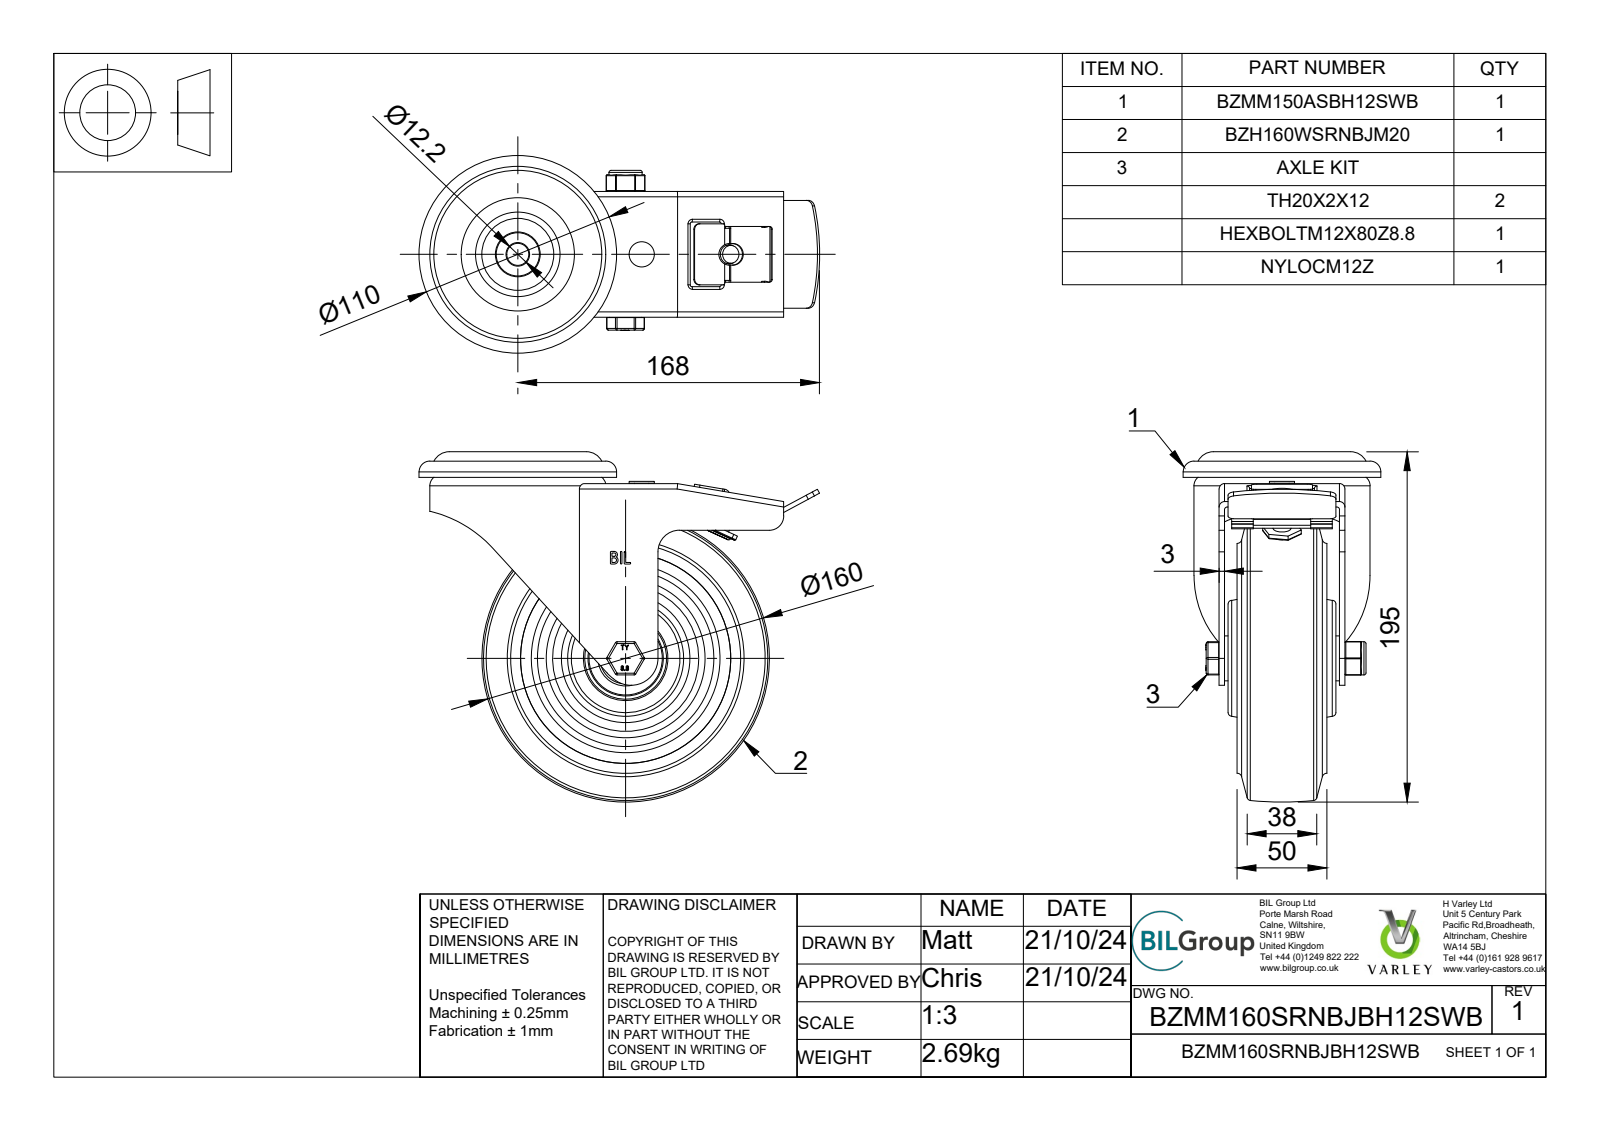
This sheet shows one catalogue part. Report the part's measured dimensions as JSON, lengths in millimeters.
{"part_name": "BZMM160SRNBJBH12SWB v3; BZMM150ASBH12SWB - 64 v1; ZINC PLATED, PRESSED STEEL TOP PLATE; ZINC PLATED, PRESSED STEEL BRAKE PEDAL (+8 more)", "step_written_by": "Autodesk Translation Framework v13.20.0.188 (AUTOMOTIVE_DESIGN)", "units": "millimeters", "bodies": {"solids": 41, "faces": 1296, "planar": 562, "cylindrical": 252, "other": 482}, "overall_size": [223, 195, 110], "volume_mm3": 943369, "surface_area_mm2": 297666, "round_holes": [[8, 2], [12.2, 2], [12, 1], [12.1, 1], [14, 1], [20, 1], [28.5, 1], [30.8, 1], [33.5, 1], [34, 1], [40, 1], [40.3, 1]], "round_bosses_or_shafts": [[25, 2], [110, 1], [77, 1], [40.8, 1], [40, 1], [31.3, 1], [27, 1], [24.5, 1]], "partial_cylinders_radius": [[0.5, 24], [1, 18], [1.5, 12], [3, 8], [2, 3], [2.5, 3], [4, 2], [6, 2]], "face_to_face_distances": [3, 67, 60, 7, 10, 5, 1.5, 4.75, 57, 1.75], "hole_center_spacings": [69]}
